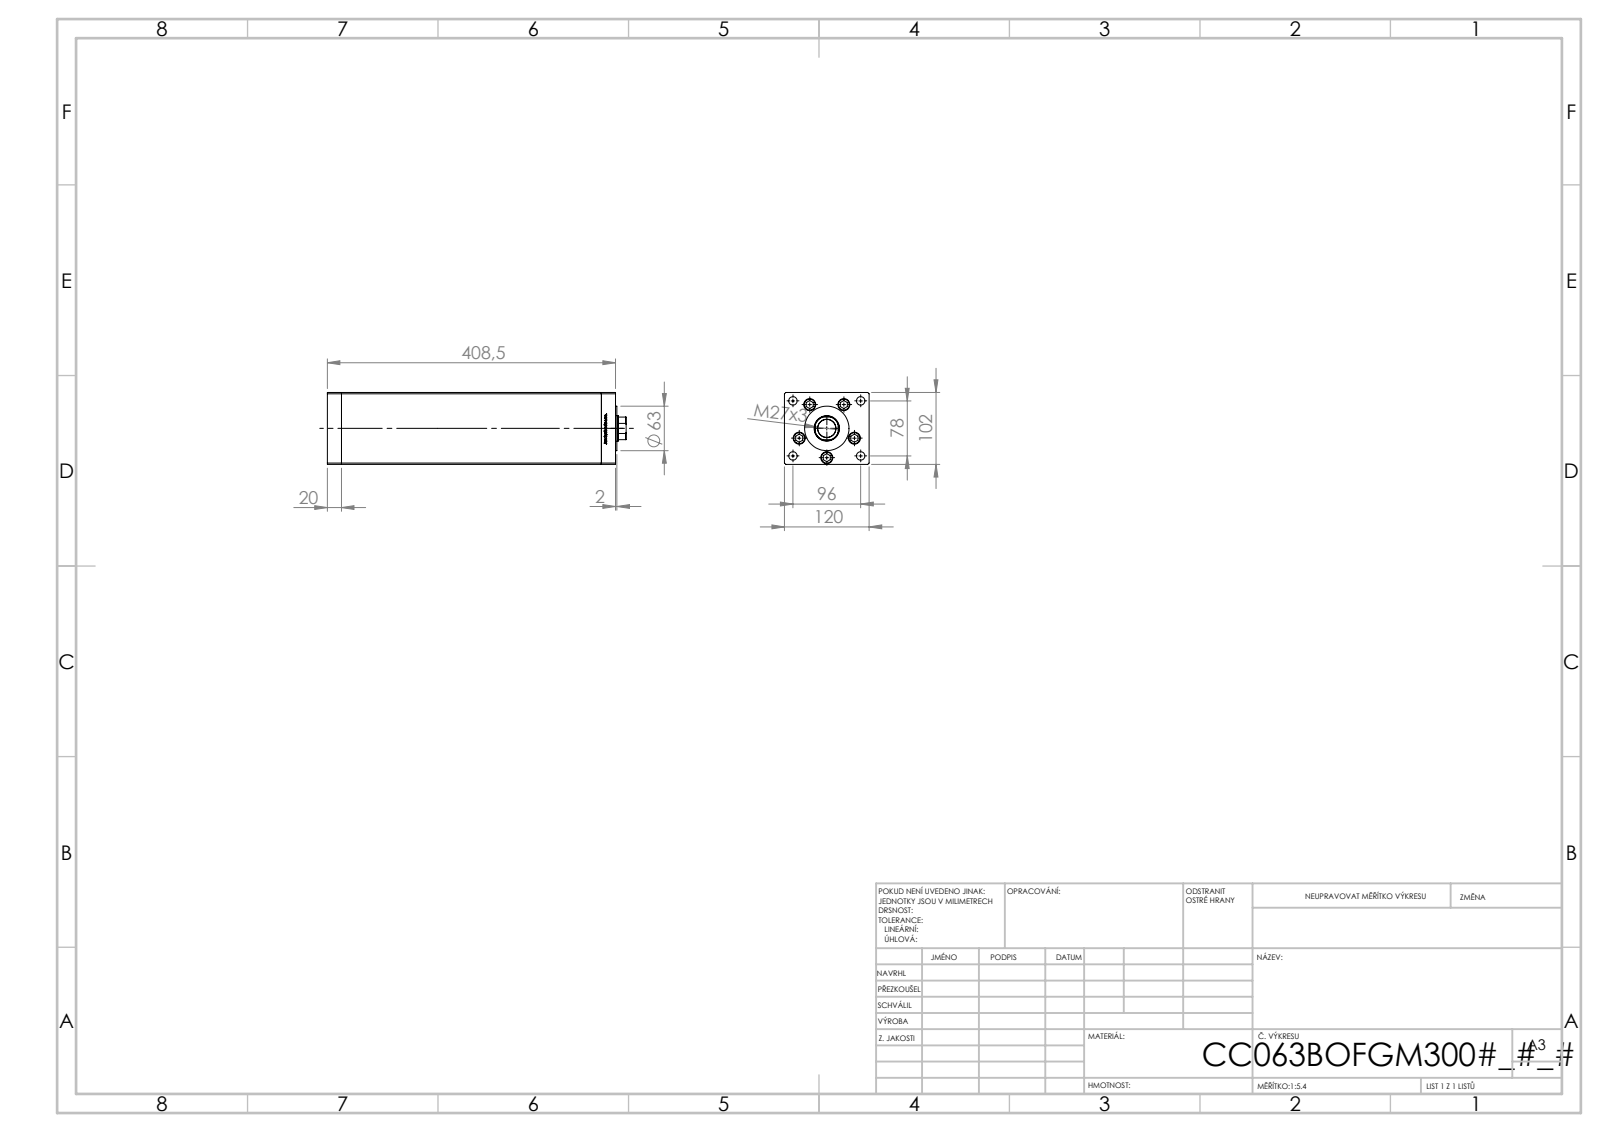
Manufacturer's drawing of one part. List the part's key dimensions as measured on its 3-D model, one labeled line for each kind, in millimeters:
Part name (STEP PRODUCT): V220C_B MIDDLE; ALLEN BOLT; V220C_VC_B; V220C_FRONT_B (+1 more)
STEP written by: SolidWorks 2019 (CONFIG_CONTROL_DESIGN)
Units: millimetres
Bodies: 14 solids, 1173 faces (460 planar, 139 cylindrical, 574 other)
Overall size (bounding box): 423.5 × 120 × 102
Volume: 4 238 000 mm³ · Surface area: 425 088 mm²
Round holes (diameter × count): ⌀13.5 ×5, ⌀17 ×5, ⌀12 ×4, ⌀25.5 ×1, ⌀36 ×1
Round bosses / shafts (diameter × count): ⌀8 ×5, ⌀63 ×1
Partial cylindrical surfaces — rounded edges, fillets, slot ends (radius × count): R0.93 ×2, R17.5 ×1
Main face-to-face distances: 120, 102, 20, 368.5, 388.5, 34.25, 408.5, 14.25, 354.25, 374.25
Hole centre spacings: 41.5, 61.85, 24.39, 26.69, 47.92, 48.07, 49.84, 53.57
